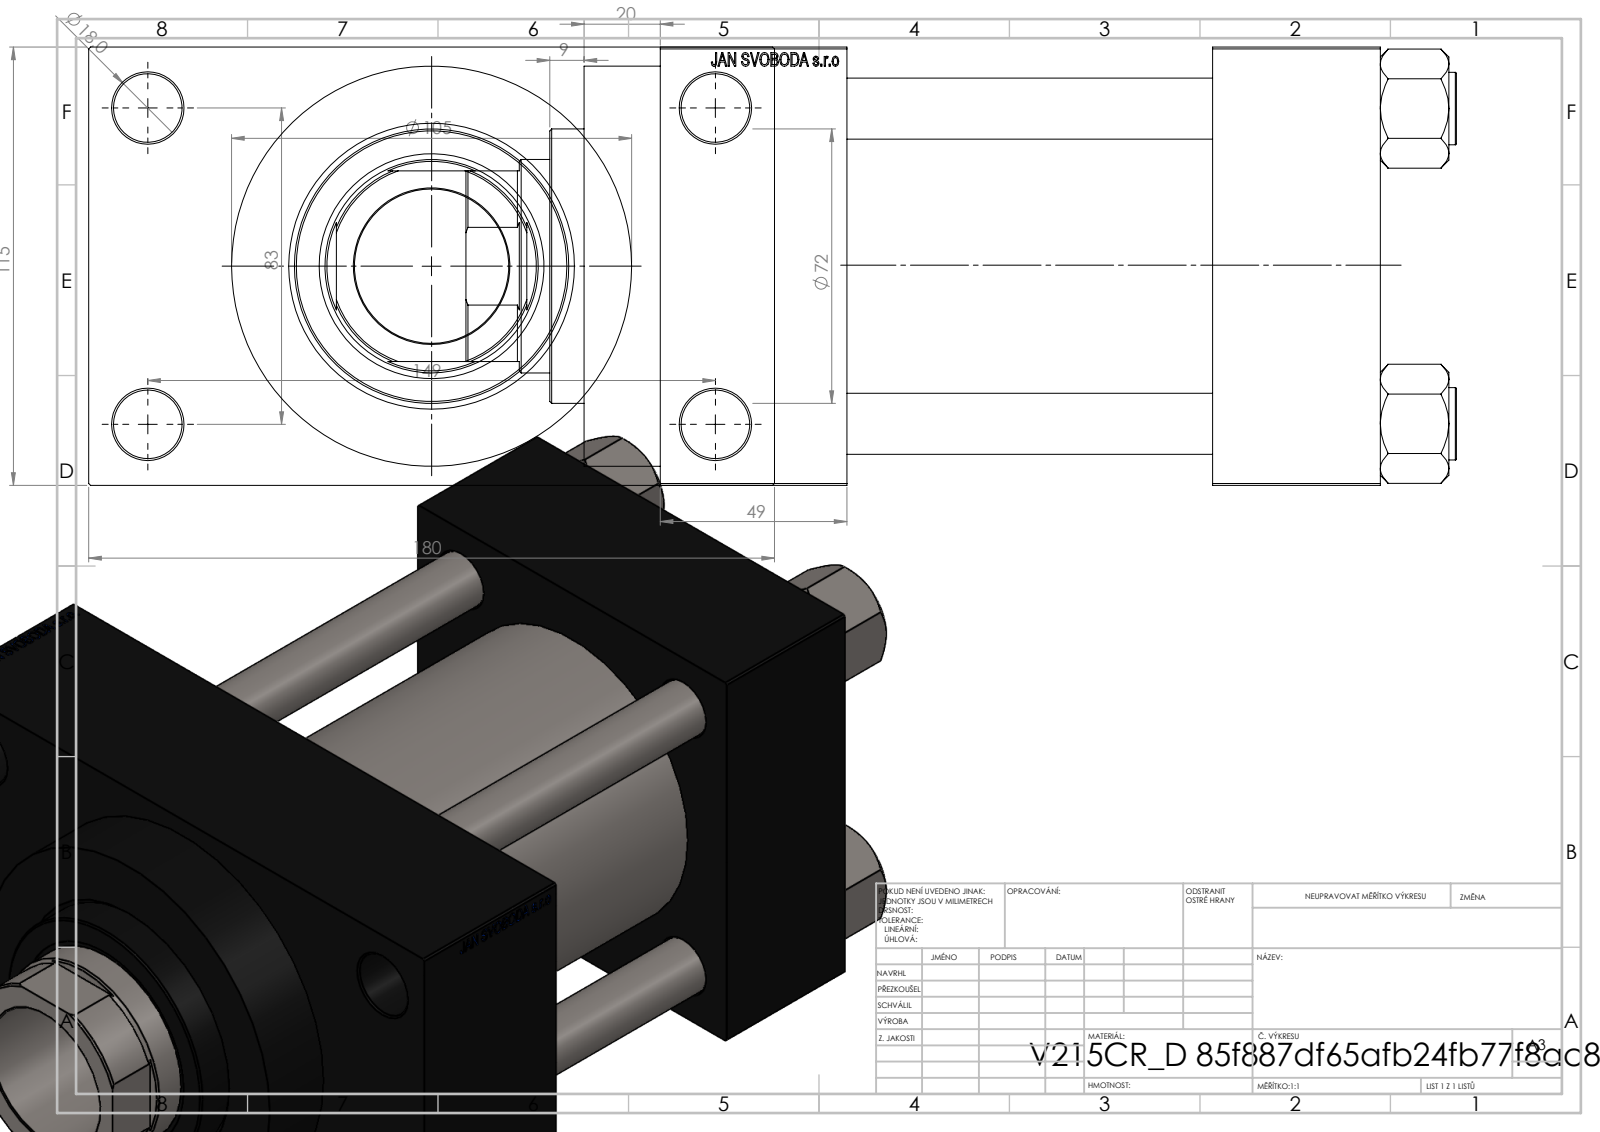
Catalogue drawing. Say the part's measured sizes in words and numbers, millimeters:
The part is named "V215CR_VCP_D; V215_VC_A; V215CR_D_TYCINKA; V215CR_D_Body (+1 more)". Its 3-D file was written by "SolidWorks 2019 (CONFIG_CONTROL_DESIGN)". It is 11 solids with 1150 faces: 544 planar, 86 cylindrical and 520 other. Overall it measures 260 by 180 by 115 millimeters. Its volume is 2 223 000 cubic millimeters and its surface area 337 495 square millimeters. Round holes: 4 of diameter 16, 4 of diameter 18, 2 of diameter 7, 2 of diameter 26.44, 2 of diameter 35, 1 of diameter 40.5, 1 of diameter 56, 1 of diameter 59, 1 of diameter 61, 1 of diameter 72, 1 of diameter 80. Round bosses or shafts: 4 of diameter 19, 1 of diameter 105, 1 of diameter 86. Partial cylindrical surfaces (rounded edges, fillets, slot ends): 1 of radius 27. The main face-to-face distances are 115, 96, 44, 140, 189, 145, 49, 32.5, 147.5, 20. The hole center spacings are 33.15, 58.48, 82.7, 85.28, 89.24, 115.85, 142.43, 83.
